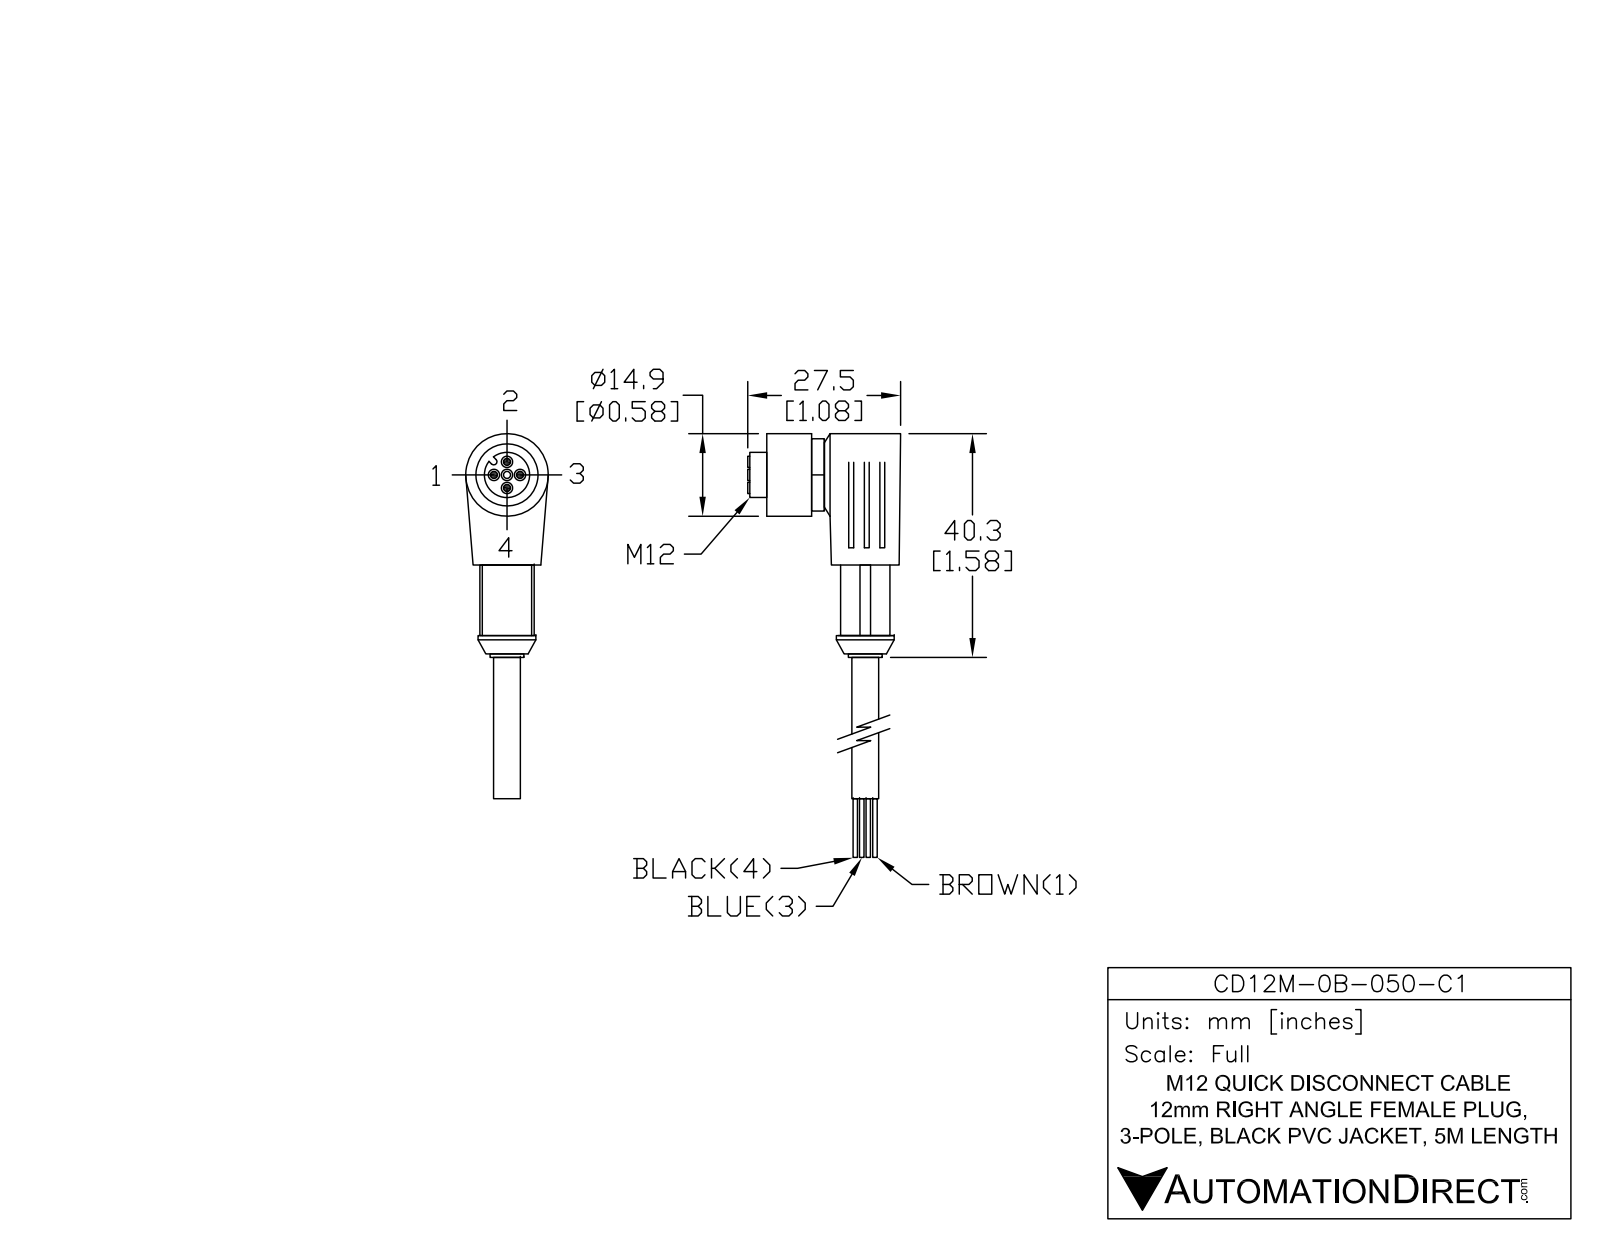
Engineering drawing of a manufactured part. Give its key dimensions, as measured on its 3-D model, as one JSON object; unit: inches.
{"part_name": "CD12M-0B-050-C1", "step_written_by": "SolidWorks 2017 (AUTOMOTIVE_DESIGN)", "units": "inches", "bodies": {"solids": 4, "faces": 326, "planar": 218, "cylindrical": 106, "other": 2}, "overall_size": [5.524, 1.083, 0.587], "volume_in3": 0.52, "surface_area_in2": 8.517, "round_holes": [[0.039, 5], [0.335, 1], [0.472, 1]], "round_bosses_or_shafts": [[0.587, 1], [0.409, 1], [0.343, 1], [0.319, 1], [0.193, 1]], "partial_cylinders_radius": [[0.022, 1]], "face_to_face_distances": [0.539, 0.5, 0.039, 0.055, 0.594, 0.094, 0.657, 0.232, 1.008, 0.508], "hole_center_spacings": [0.093, 0.131, 0.185]}
